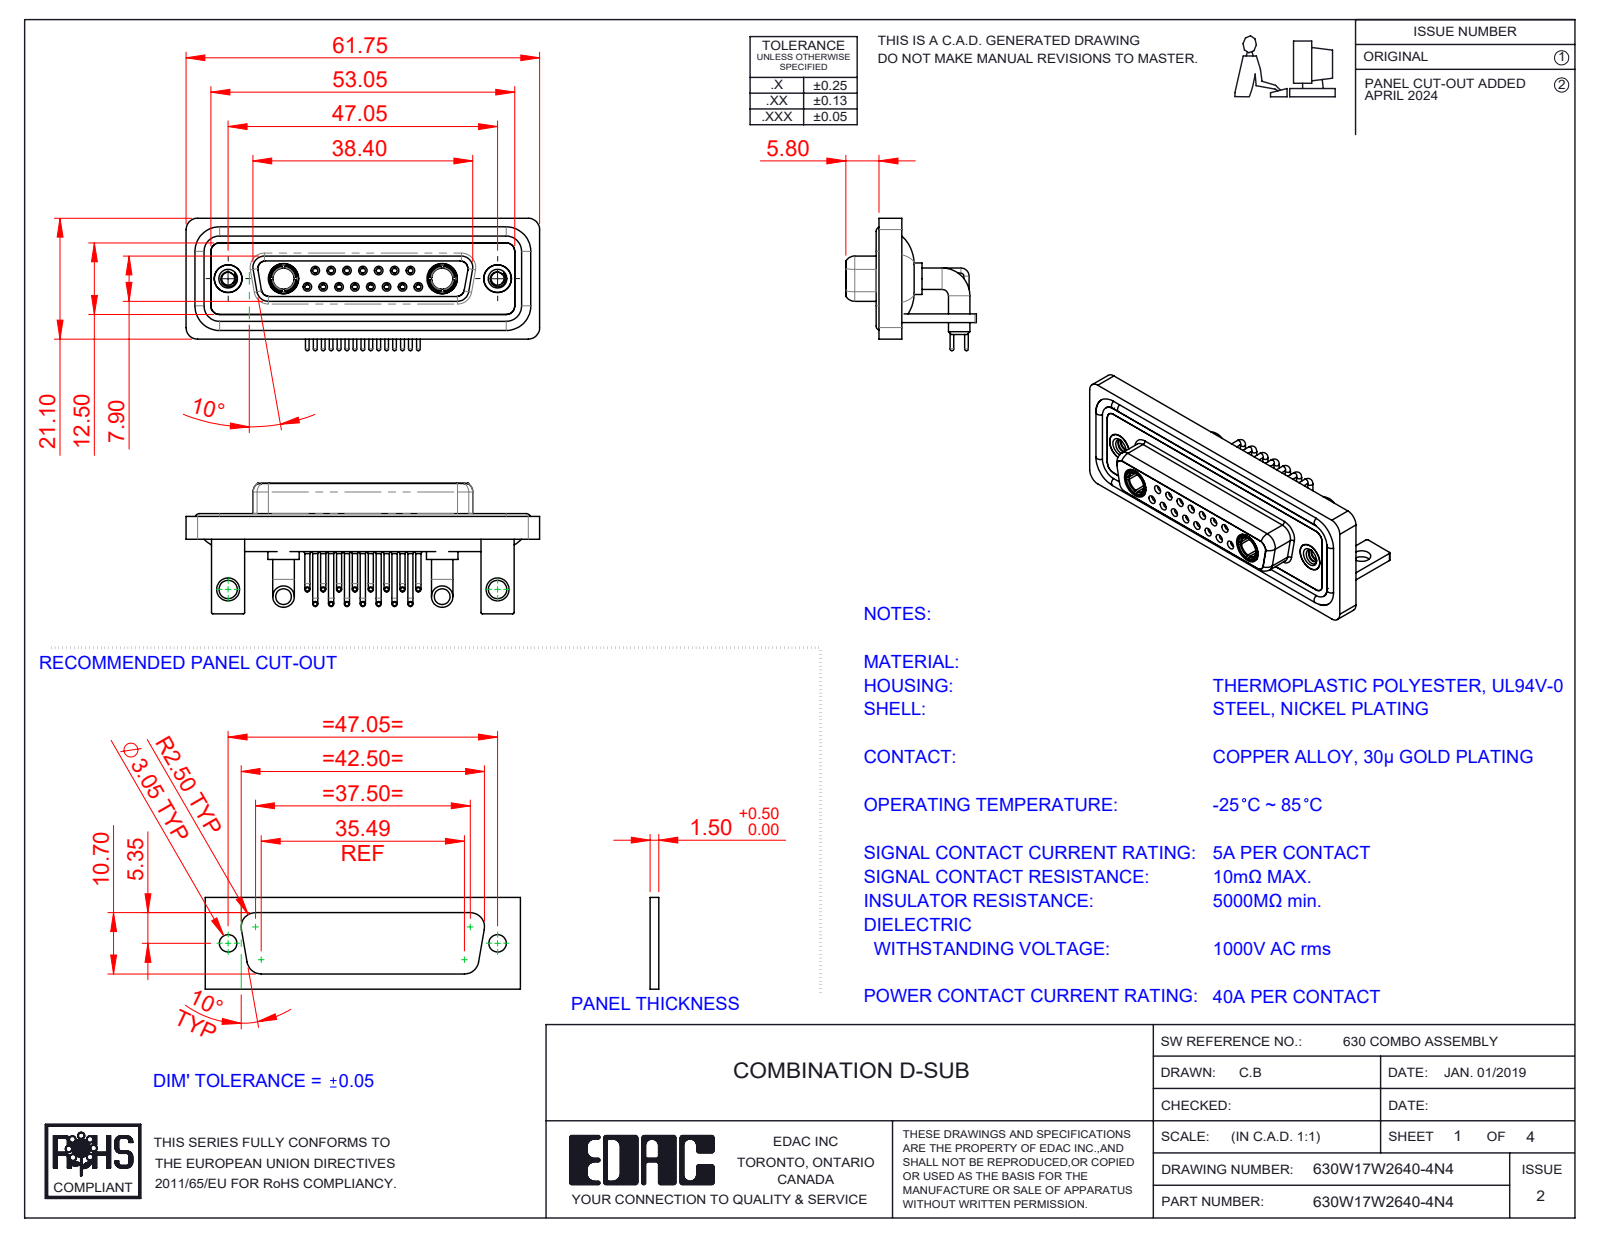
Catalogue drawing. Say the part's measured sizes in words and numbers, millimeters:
The part is named "630W17W2640-4N4; 630Combo Stabilizer Bracket_50 Contacts; 630Combo Shell Front_25 Contacts; 630Combo Shell Rear_25 Contacts (+6 more)". Its 3-D file was written by "SolidWorks 2023 (CONFIG_CONTROL_DESIGN)". It is 28 solids with 1385 faces: 408 planar, 607 cylindrical and 370 other. Overall it measures 61.75 by 23.12 by 22.8 millimeters. Its volume is 8 999 cubic millimeters and its surface area 15 353 square millimeters. Round holes: 15 of diameter 0.9, 15 of diameter 1.1, 15 of diameter 1.5, 15 of diameter 2, 8 of diameter 1.6, 7 of diameter 1.7, 4 of diameter 4.85, 2 of diameter 2.26, 2 of diameter 3.2, 2 of diameter 3.7, 2 of diameter 4, 2 of diameter 4.05. Round bosses or shafts: 15 of diameter 0.9, 15 of diameter 0.65, 11 of diameter 1.6, 4 of diameter 3.75, 2 of diameter 5.5, 2 of diameter 5.2, 2 of diameter 4.96, 2 of diameter 4.95. Partial cylindrical surfaces (rounded edges, fillets, slot ends): 19 of radius 2, 18 of radius 1.5, 16 of radius 0.25, 8 of radius 1.35, 8 of radius 1.6, 5 of radius 0.5, 4 of radius 0.6, 4 of radius 0.65. The main face-to-face distances are 0.4, 1.8, 2.9, 3.7, 1.5, 4.1, 1.1, 1.4, 1.6, 3.1. The hole center spacings are 3.16, 2.77, 5.54, 8.31, 5.04, 7.49, 11.08, 5.03.
